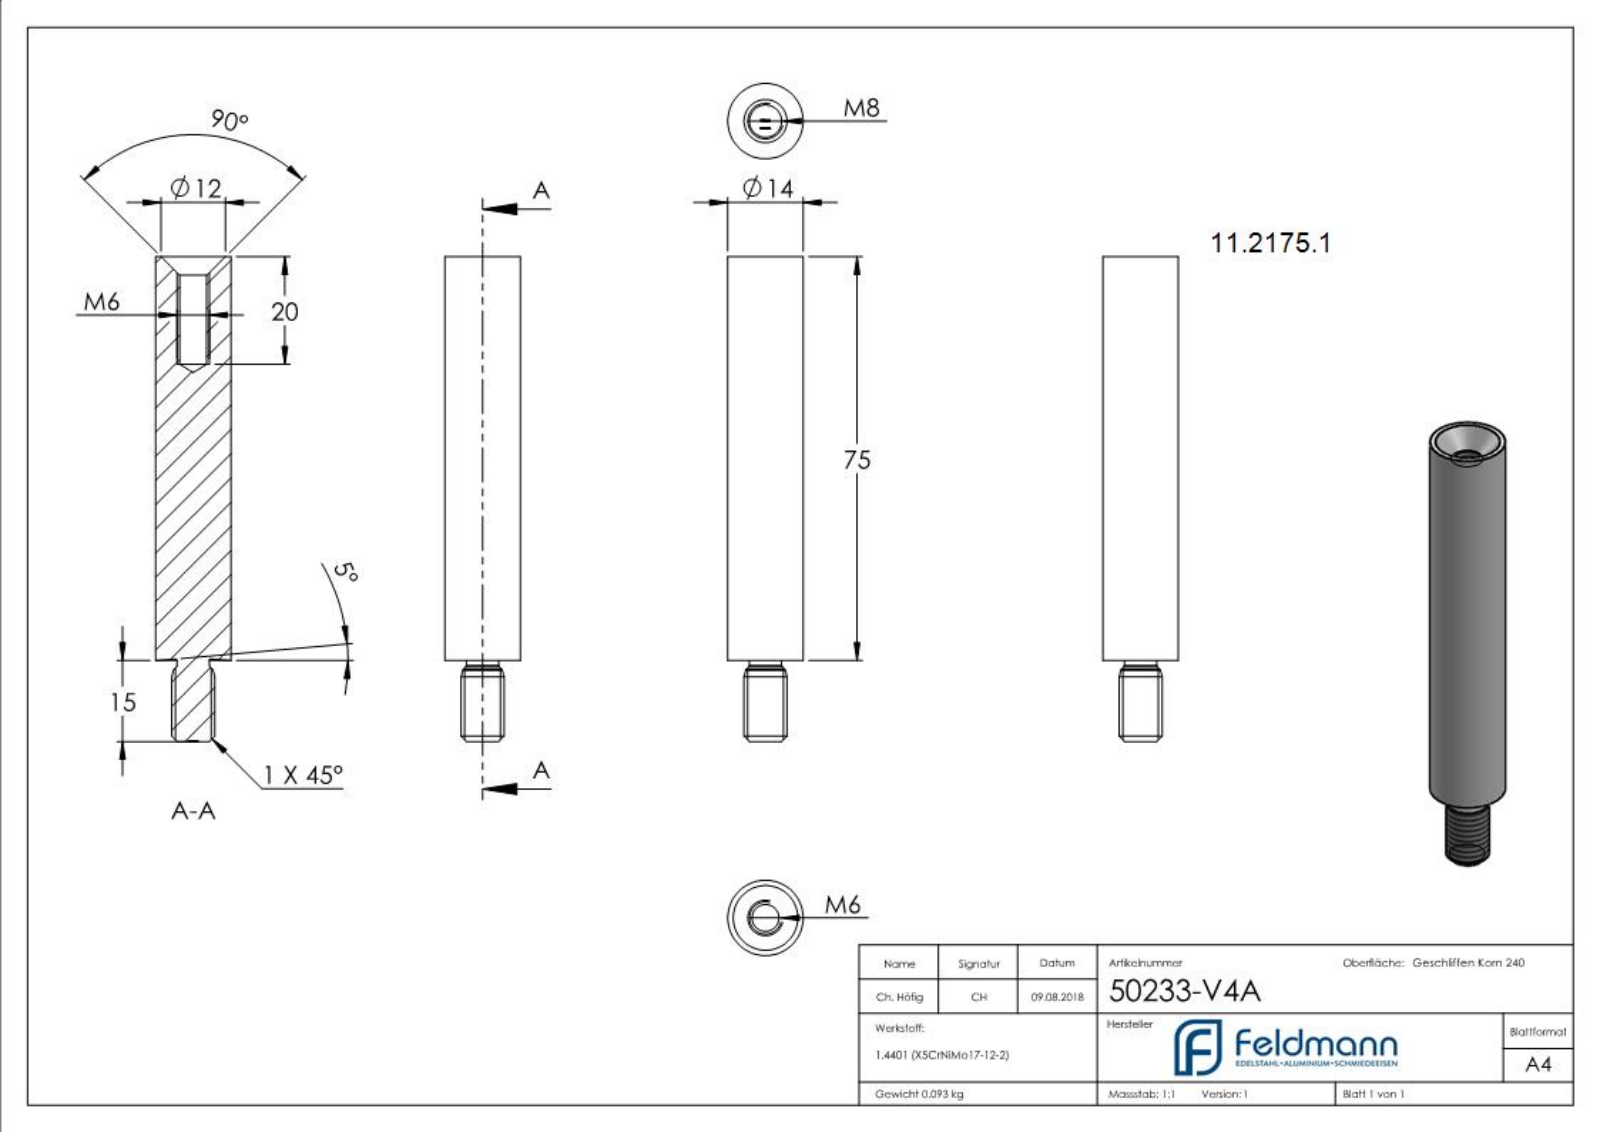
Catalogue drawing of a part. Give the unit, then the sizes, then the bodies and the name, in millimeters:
Units: millimetres
Overall size (bounding box): 90 × 14 × 14
Round holes (diameter × count): ⌀5 ×1
Round bosses / shafts (diameter × count): ⌀14 ×1, ⌀8 ×1
Main face-to-face distances: 90, 89.9, 0.77, 1.29, 2.38, 2.39, 0.72, 1.55, 2.44, 0.57
Volume: 11 688 mm³ · Surface area: 4 322 mm²
Bodies: 1 solid, 269 faces (157 planar, 3 cylindrical, 109 other)
Part name (STEP PRODUCT): 50233-V4A
STEP written by: SolidWorks 2018 (CONFIG_CONTROL_DESIGN)
